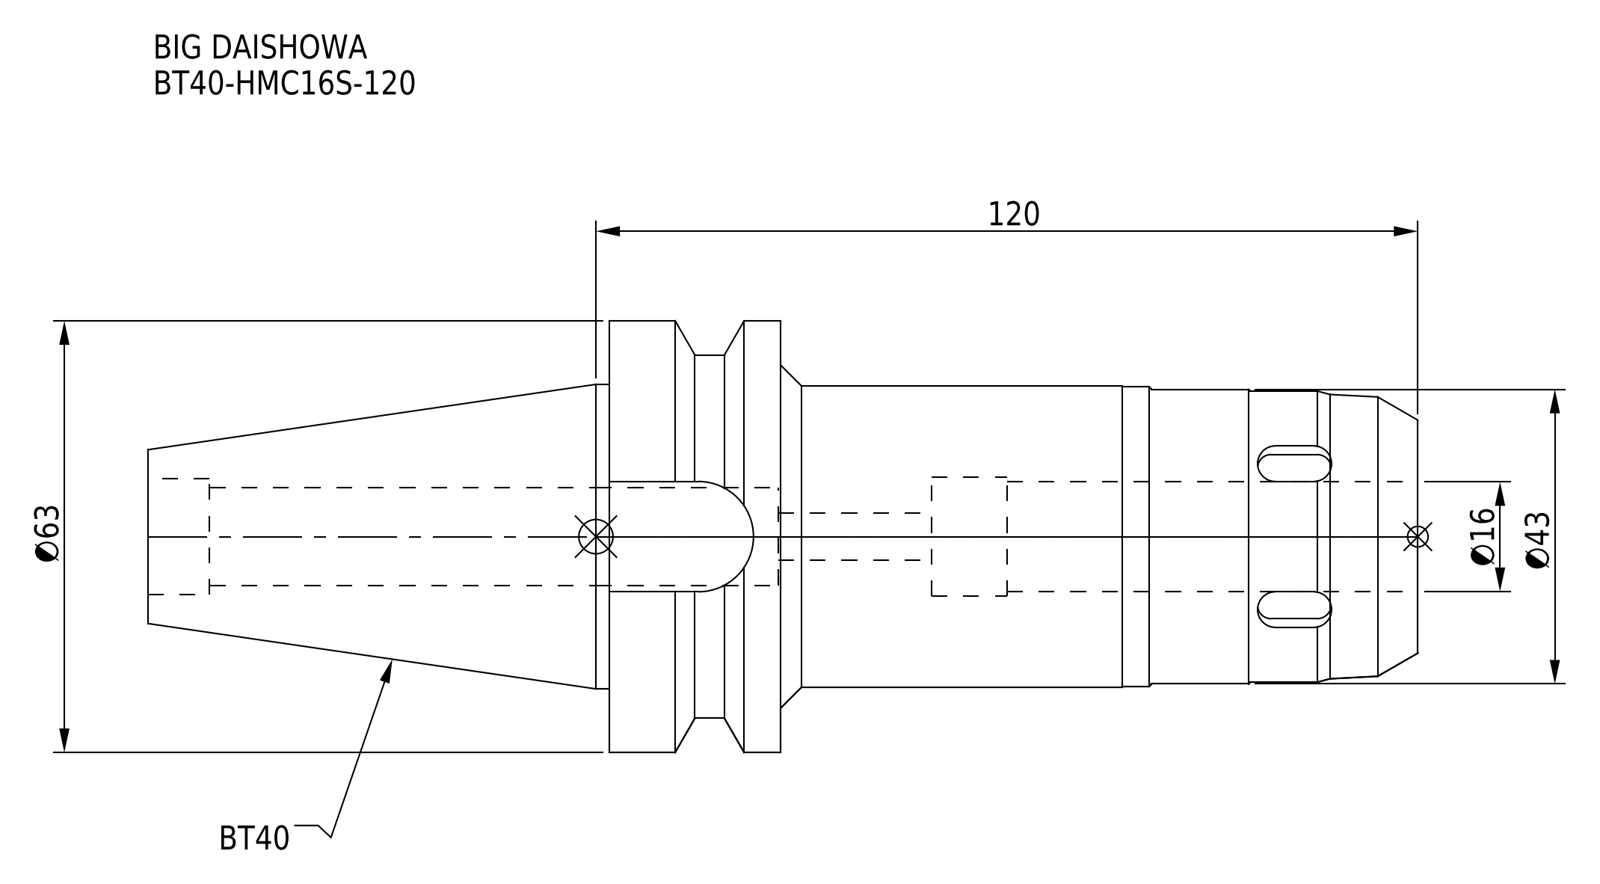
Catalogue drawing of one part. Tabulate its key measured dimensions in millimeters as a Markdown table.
| quantity | value |
| --- | --- |
| part name | BT40-HMC16S-120 |
| STEP written by | CREO PARAMETRIC BY PTC INC, 2016380 (AUTOMOTIVE_DESIGN) |
| units | millimeters |
| bodies | 1 solid, 95 faces (33 planar, 40 cylindrical, 22 other) |
| overall size | 185.4 × 63 × 63 |
| volume | 238 807 mm³ |
| surface area | 39 233 mm² |
| round holes (diameter × count) | 6.8 × 1, 14.2 × 1, 16 × 1, 17 × 1, 17.4 × 1 |
| round bosses / shafts (diameter × count) | 63 × 1, 53 × 1, 44.45 × 1, 44 × 1, 43.7 × 1, 43 × 1, 42.5 × 1 |
| partial cylindrical surfaces (radius × count) | 3 × 6, 8.05 × 1 |
| main face-to-face distances | 25, 93, 118, 45, 185.4, 92.4, 67.4, 71, 22, 47 |
